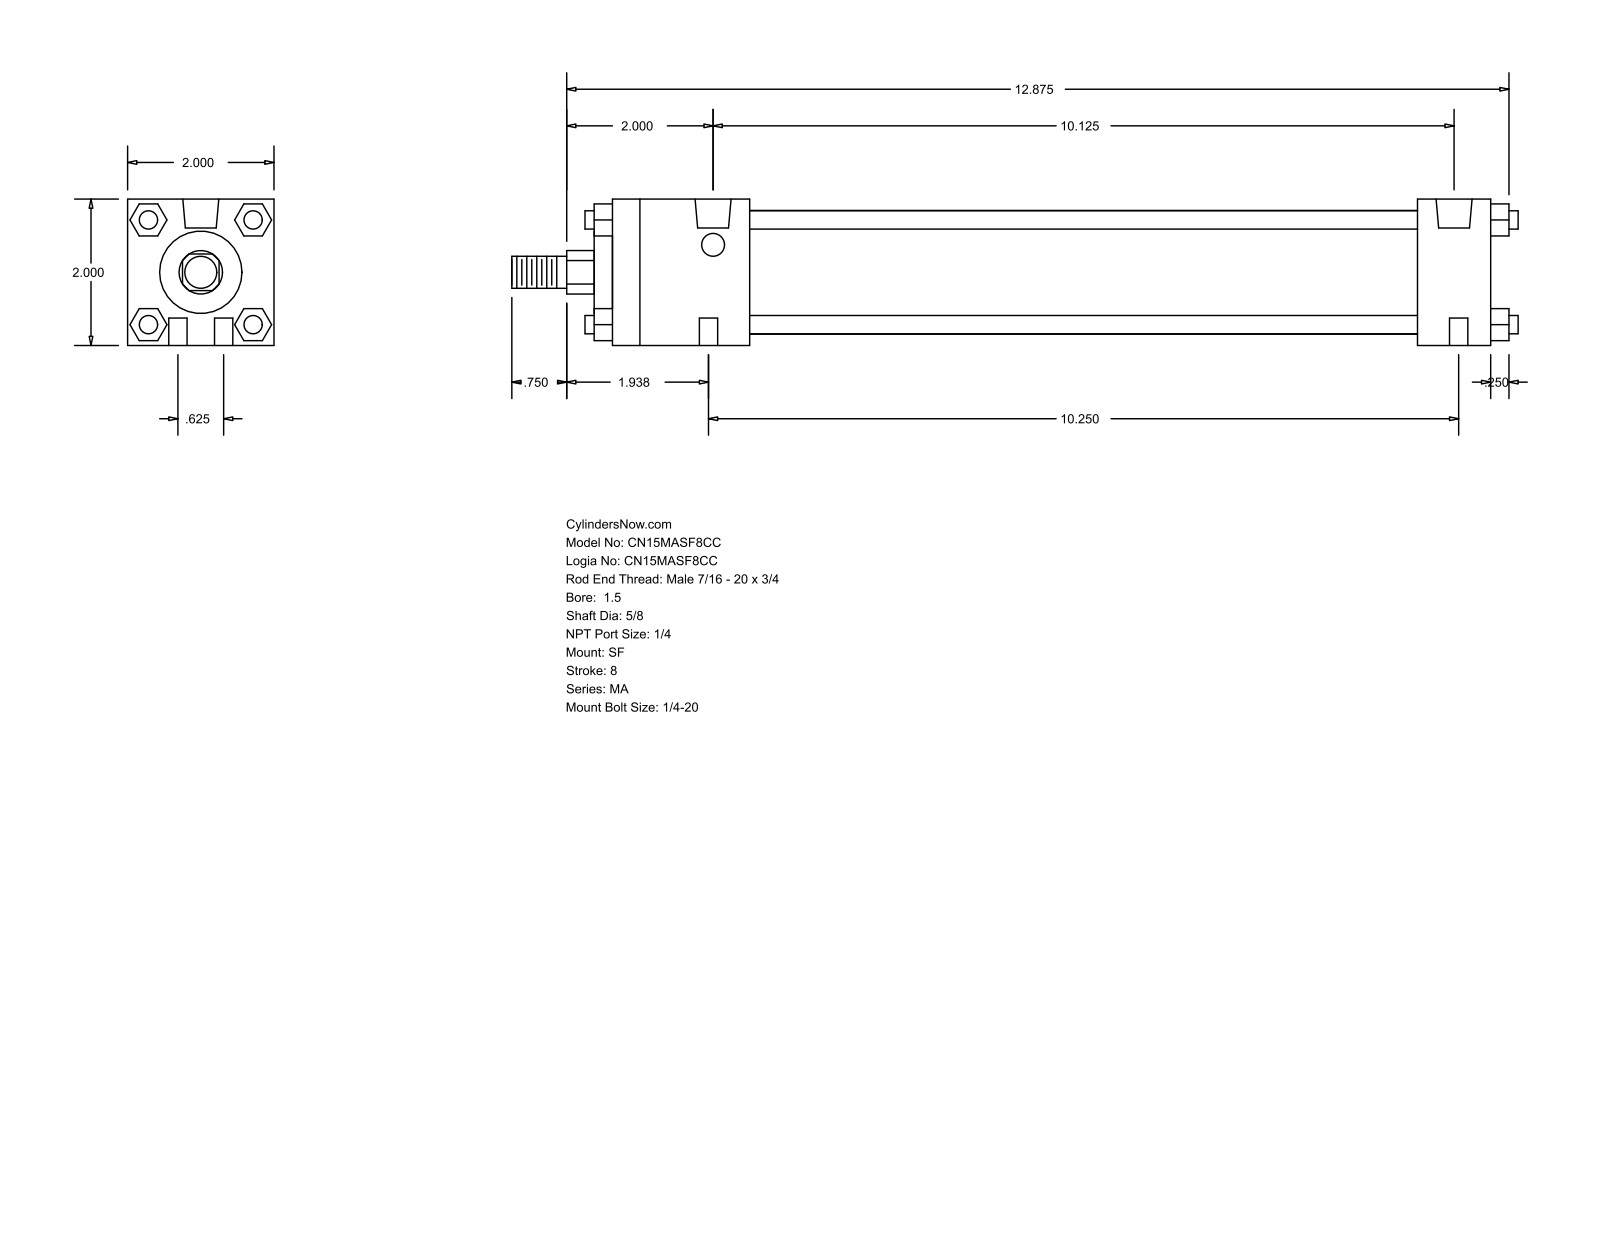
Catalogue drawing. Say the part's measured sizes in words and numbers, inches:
The part is named "MA_SF__0150_0.625". Its 3-D file was written by "GSSL Pune (CONFIG_CONTROL_DESIGN)". It is 0 solids with 124 faces: 94 planar, 30 cylindrical and 0 other. Overall it measures 13.75 by 2 by 2 inches. Round holes: 4 of diameter 0.25, 2 of diameter 0.313, 2 of diameter 0.492. Round bosses or shafts: 4 of diameter 0.25, 1 of diameter 1.69, 1 of diameter 1.125, 1 of diameter 0.625, 1 of diameter 0.437. Partial cylindrical surfaces (rounded edges, fillets, slot ends): 1 of radius 0.297. The main face-to-face distances are 2, 12, 1.875, 11, 9.125, 10.125, 1, 0.25, 2.125, 11.25. The hole center spacings are 0.319, 0.625, 10.125, 10.192, 10.193, 10.25, 10.269.
